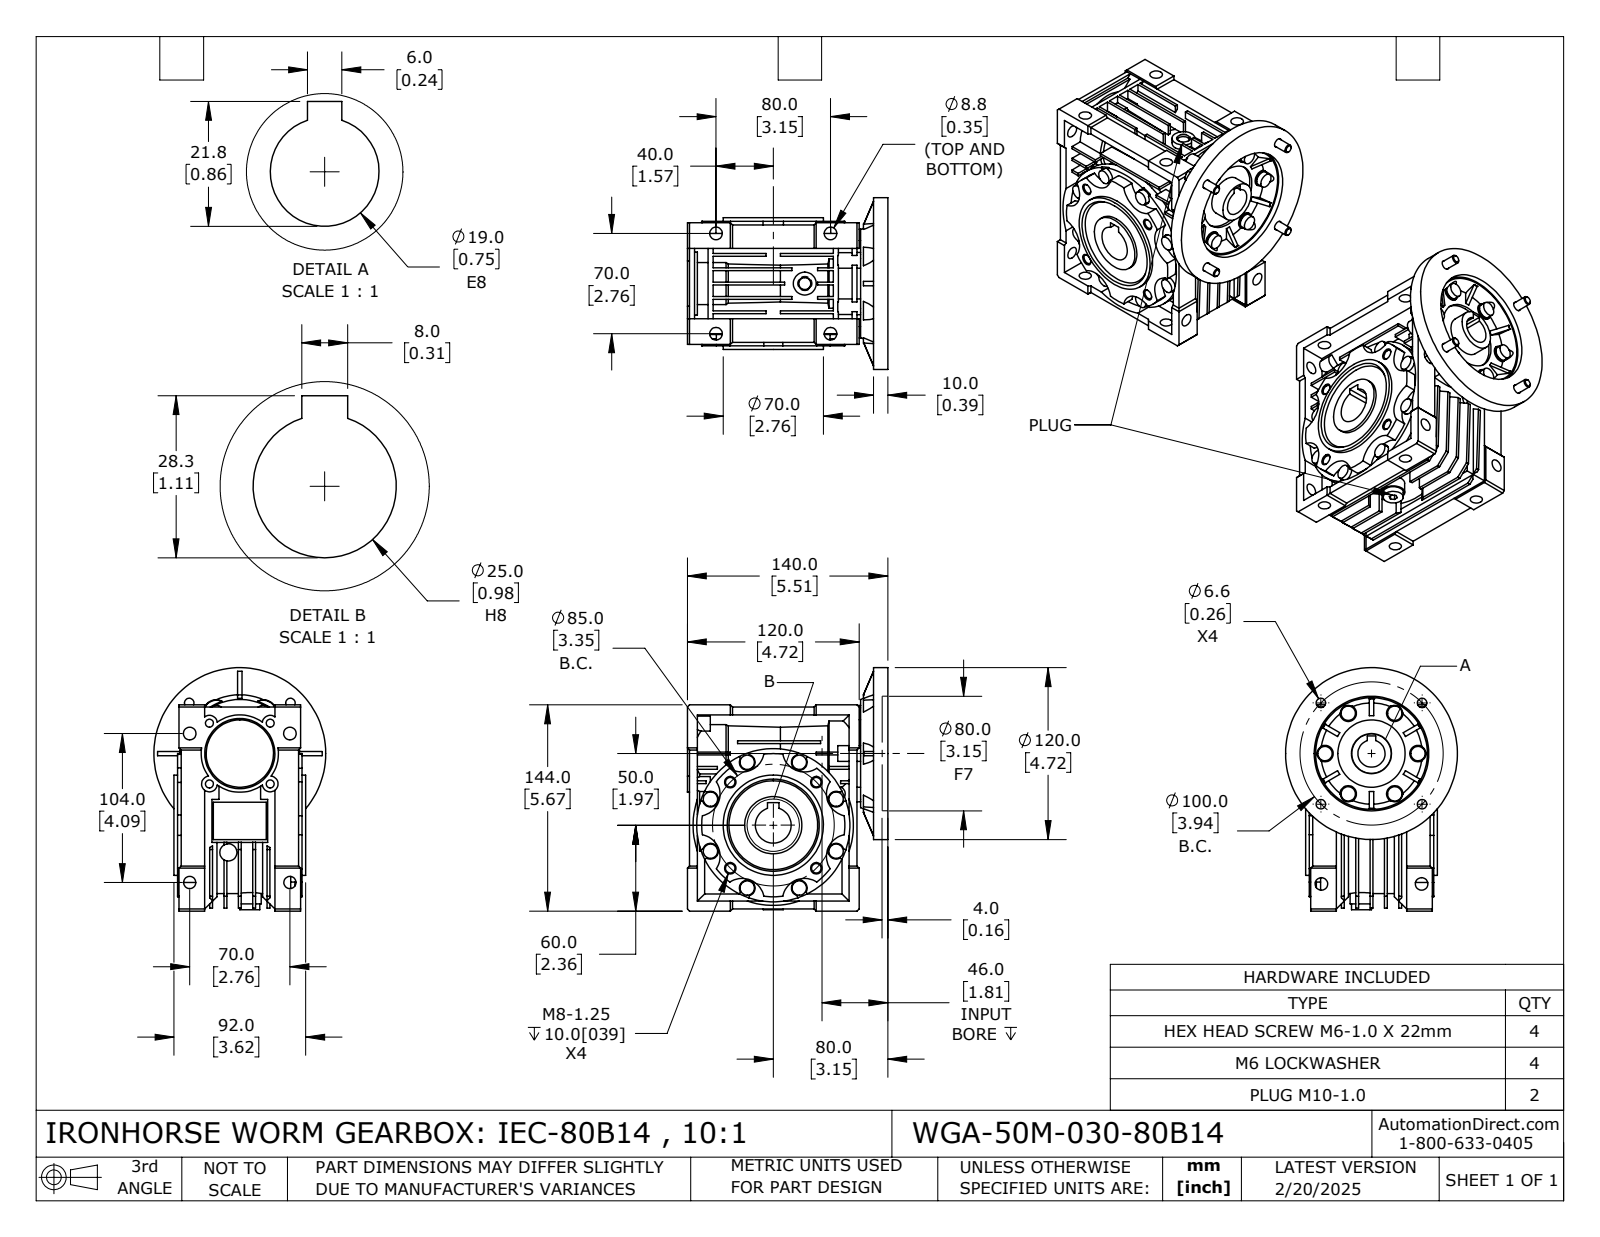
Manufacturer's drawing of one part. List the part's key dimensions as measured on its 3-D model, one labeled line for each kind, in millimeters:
Part name (STEP PRODUCT): WGA-50M-030-80B14
STEP written by: SolidWorks 2024 (CONFIG_CONTROL_DESIGN)
Units: millimetres
Bodies: 14 solids, 1080 faces (600 planar, 339 cylindrical, 141 other)
Overall size (bounding box): 170 × 150.5 × 120
Volume: 1 088 000 mm³ · Surface area: 242 203 mm²
Round holes (diameter × count): ⌀8.8 ×8, ⌀8.5 ×6, ⌀5.55 ×4, ⌀6.1 ×4, ⌀6.6 ×4, ⌀6.65 ×2, ⌀6.65 ×2, ⌀9 ×2, ⌀19 ×1, ⌀20 ×1, ⌀25 ×1, ⌀28 ×1
Round bosses / shafts (diameter × count): ⌀10 ×14, ⌀12.2 ×4, ⌀6 ×4, ⌀16 ×2, ⌀120 ×1, ⌀107 ×1, ⌀70 ×1, ⌀61 ×1
Partial cylindrical surfaces — rounded edges, fillets, slot ends (radius × count): R5.5 ×18, R6 ×8, R15 ×8, R15.5 ×8, R5.75 ×6, R20.76 ×1, R46 ×1, R47.7 ×1
Main face-to-face distances: 10, 2, 7, 1.5, 8, 5.5, 20, 2.5, 55, 35
Hole centre spacings: 58.31, 80, 70, 20.01, 30, 42.42, 42.5, 50.01
